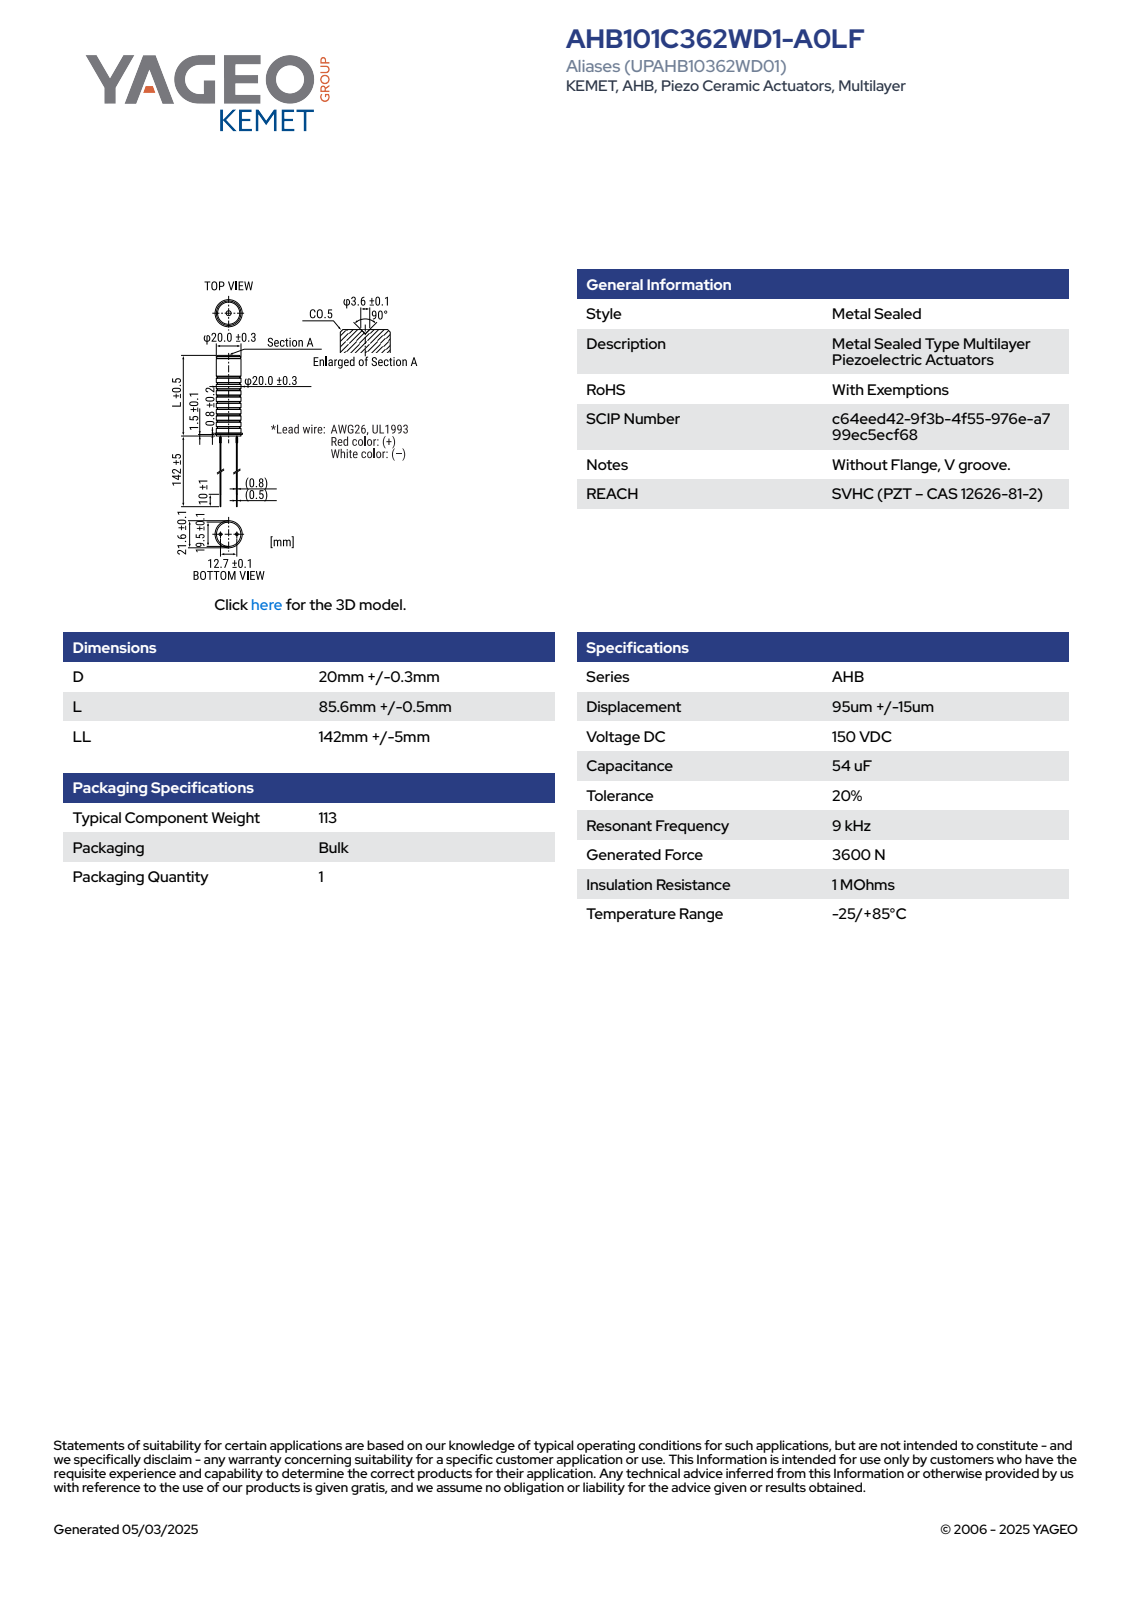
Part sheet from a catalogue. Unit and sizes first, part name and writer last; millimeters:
Units: millimetres
Overall size (bounding box): 233.1 × 21.7 × 21.7
Round bosses / shafts (diameter × count): ⌀1 ×2, ⌀0.8 ×2, ⌀21.7 ×1, ⌀20.3 ×1, ⌀19.6 ×1, ⌀0.6 ×1, ⌀0.5 ×1
Main face-to-face distances: 83.5, 2.6, 86.1, 1.6, 1, 84.5, 86.11, 84.51, 83.51, 10
Volume: 27 258 mm³ · Surface area: 8 095 mm²
Bodies: 2 solids, 131 faces (65 planar, 34 cylindrical, 32 other)
Part name (STEP PRODUCT): AL_KAHBASB_D20.3L86.1
STEP written by: SolidWorks 2021 (AUTOMOTIVE_DESIGN)
